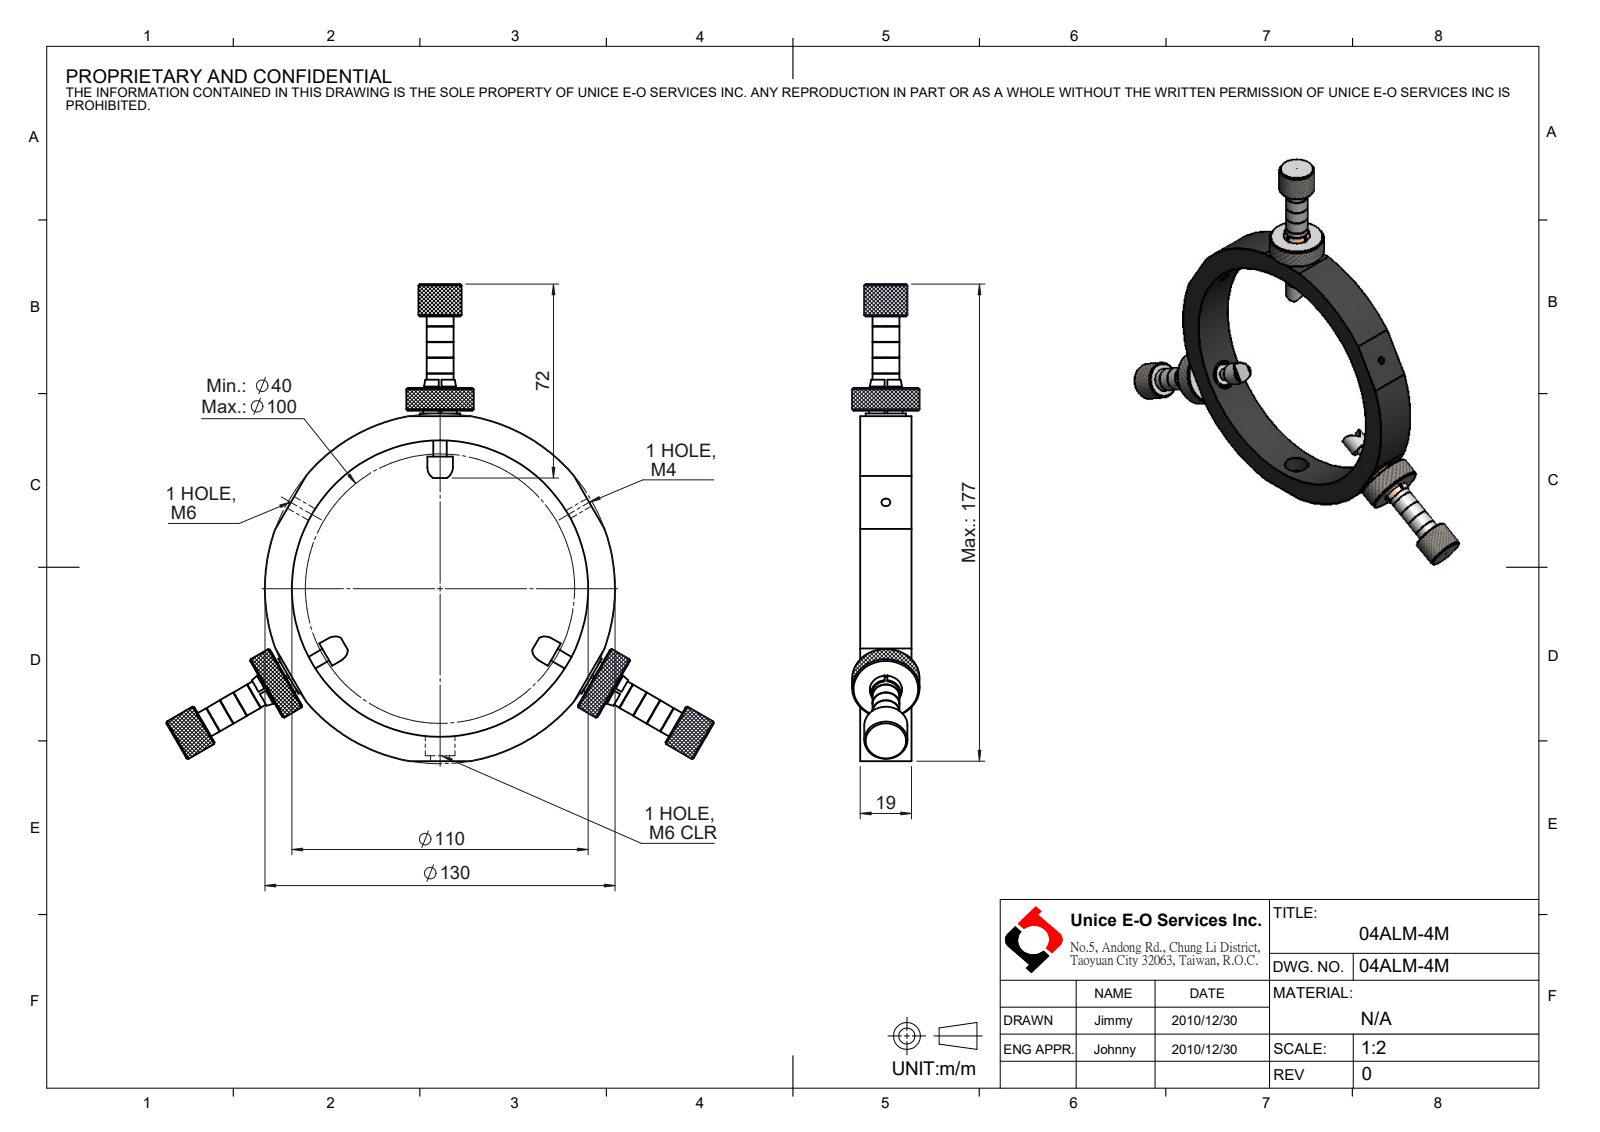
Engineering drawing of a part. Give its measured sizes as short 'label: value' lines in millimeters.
name: 04ALM-4M
written by: SolidWorks 2016 (CONFIG_CONTROL_DESIGN)
unit: mm
bodies: 16 solids, 469 faces (171 planar, 238 cylindrical, 60 other)
size: 203.22 × 177 × 25
volume: 95 270 mm³; area: 50 307 mm²
holes: 3× ⌀5.25, 3× ⌀8, 3× ⌀11, 3× ⌀12.7, 1× ⌀3.3, 1× ⌀7, 1× ⌀110
bosses: 3× ⌀25, 3× ⌀16, 3× ⌀15, 3× ⌀12.5, 3× ⌀12, 3× ⌀10, 3× ⌀9.5, 3× ⌀9
rounds: 1× R65
face distances: 19, 2, 8.5, 10.5, 128, 138.5, 130, 38.5, 47, 10
